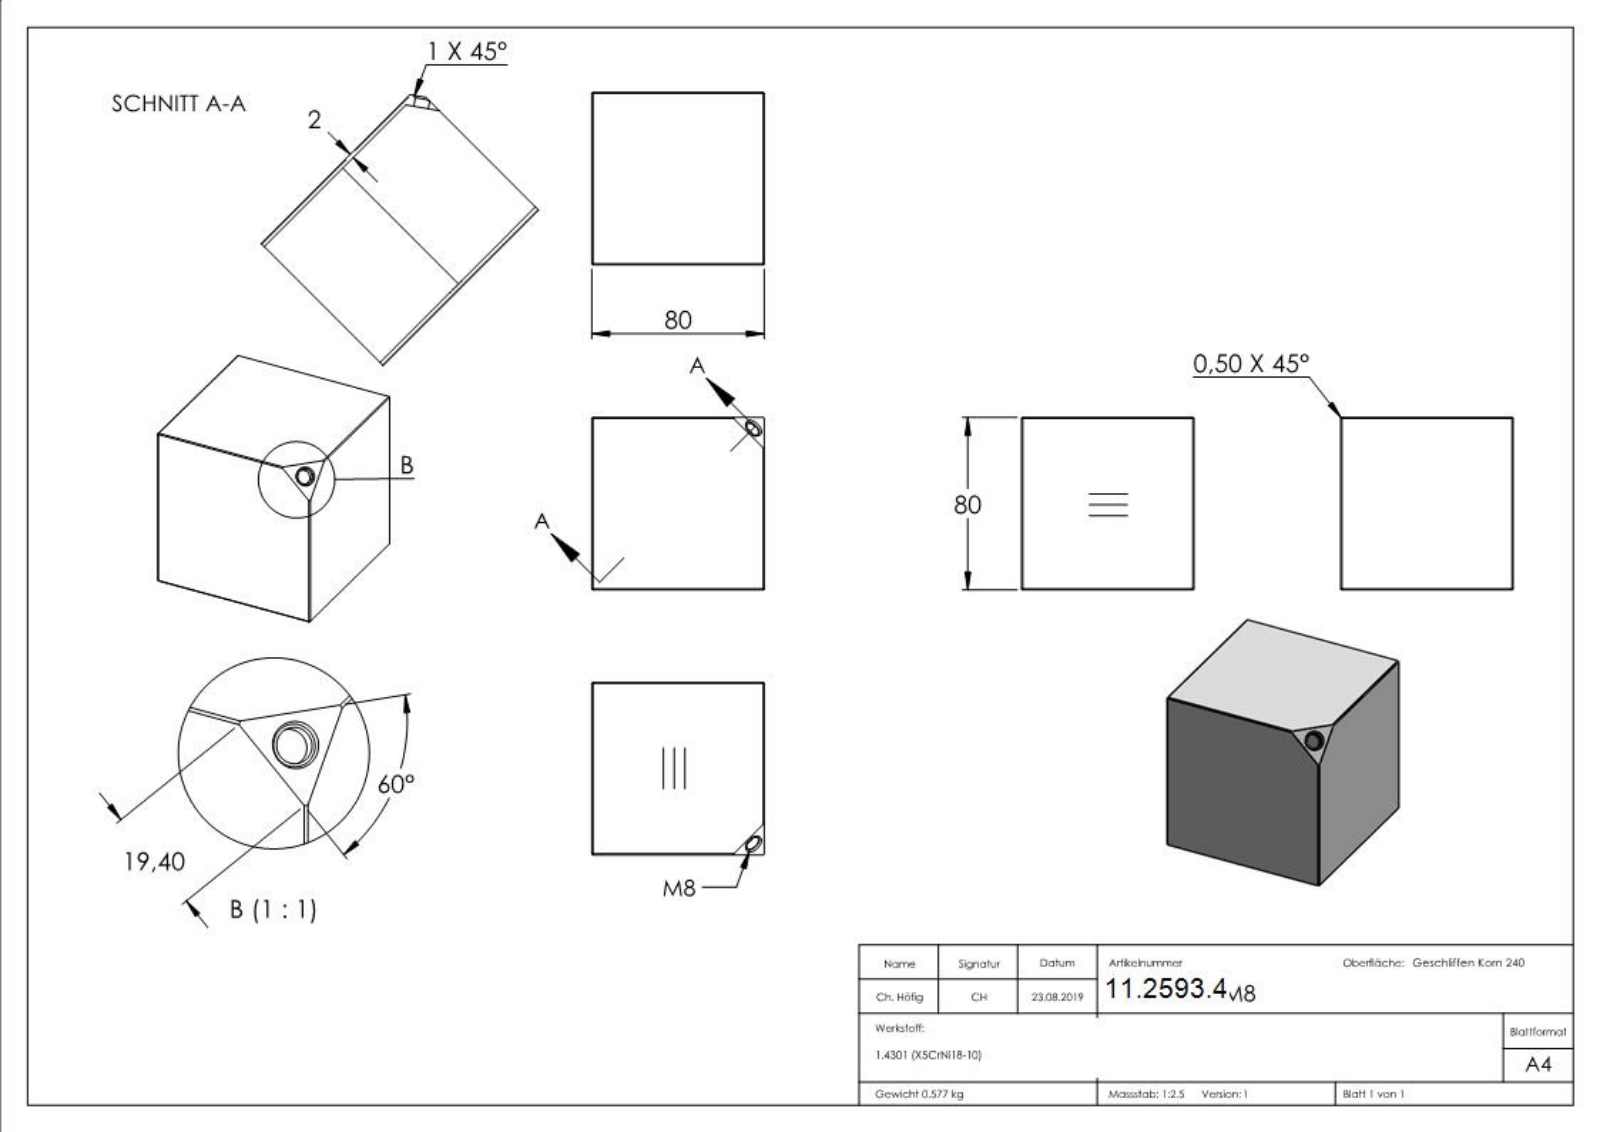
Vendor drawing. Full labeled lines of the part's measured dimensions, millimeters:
Part name (STEP PRODUCT): 166-80-VA-M8
STEP written by: SolidWorks 2015 (CONFIG_CONTROL_DESIGN)
Units: millimetres
Bodies: 1 solid, 286 faces (173 planar, 2 cylindrical, 111 other)
Overall size (bounding box): 80 × 80 × 80
Volume: 73 060 mm³ · Surface area: 72 492 mm²
Round holes (diameter × count): ⌀6.8 ×1
Main face-to-face distances: 2, 78, 80, 76, 112.42, 5, 1.9, 76.1, 78.1, 137.32
